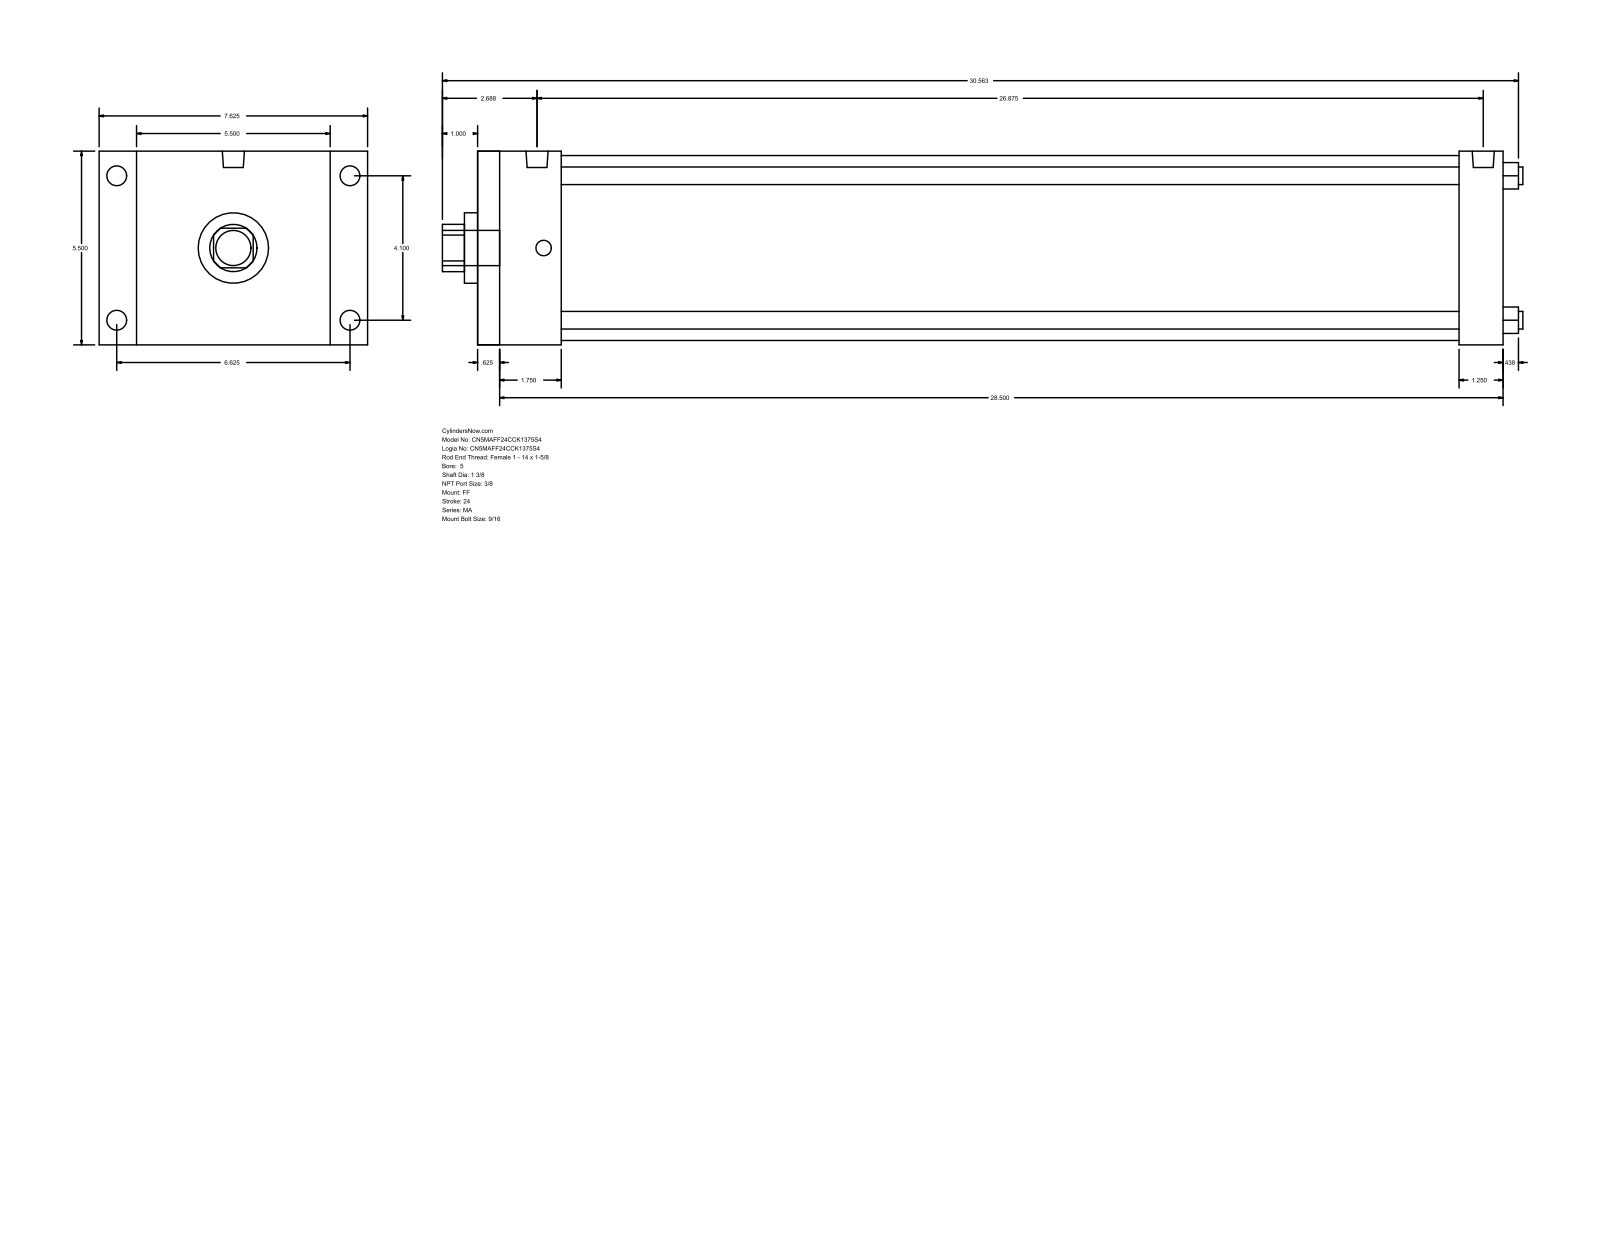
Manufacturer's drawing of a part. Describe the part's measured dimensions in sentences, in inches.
The part is named "MA_FF__0500_1.375". Its 3-D file was written by "GSSL Pune (CONFIG_CONTROL_DESIGN)". It is 0 solids with 92 faces: 64 planar, 28 cylindrical and 0 other. Overall it measures 30.687 by 7.625 by 5.5 inches. Round holes: 4 of diameter 0.5, 1 of diameter 1.375, 1 of diameter 2, 1 of diameter 5.25. Round bosses or shafts: 4 of diameter 0.563, 4 of diameter 0.437, 2 of diameter 0.627, 1 of diameter 1. Partial cylindrical surfaces (rounded edges, fillets, slot ends): 1 of radius 0.672. The main face-to-face distances are 5.5, 29.125, 0.625, 28.5, 27.875, 27.25, 1.25, 2.375, 1.75, 25.5. The hole center spacings are 2.899, 4.1, 5.798.
